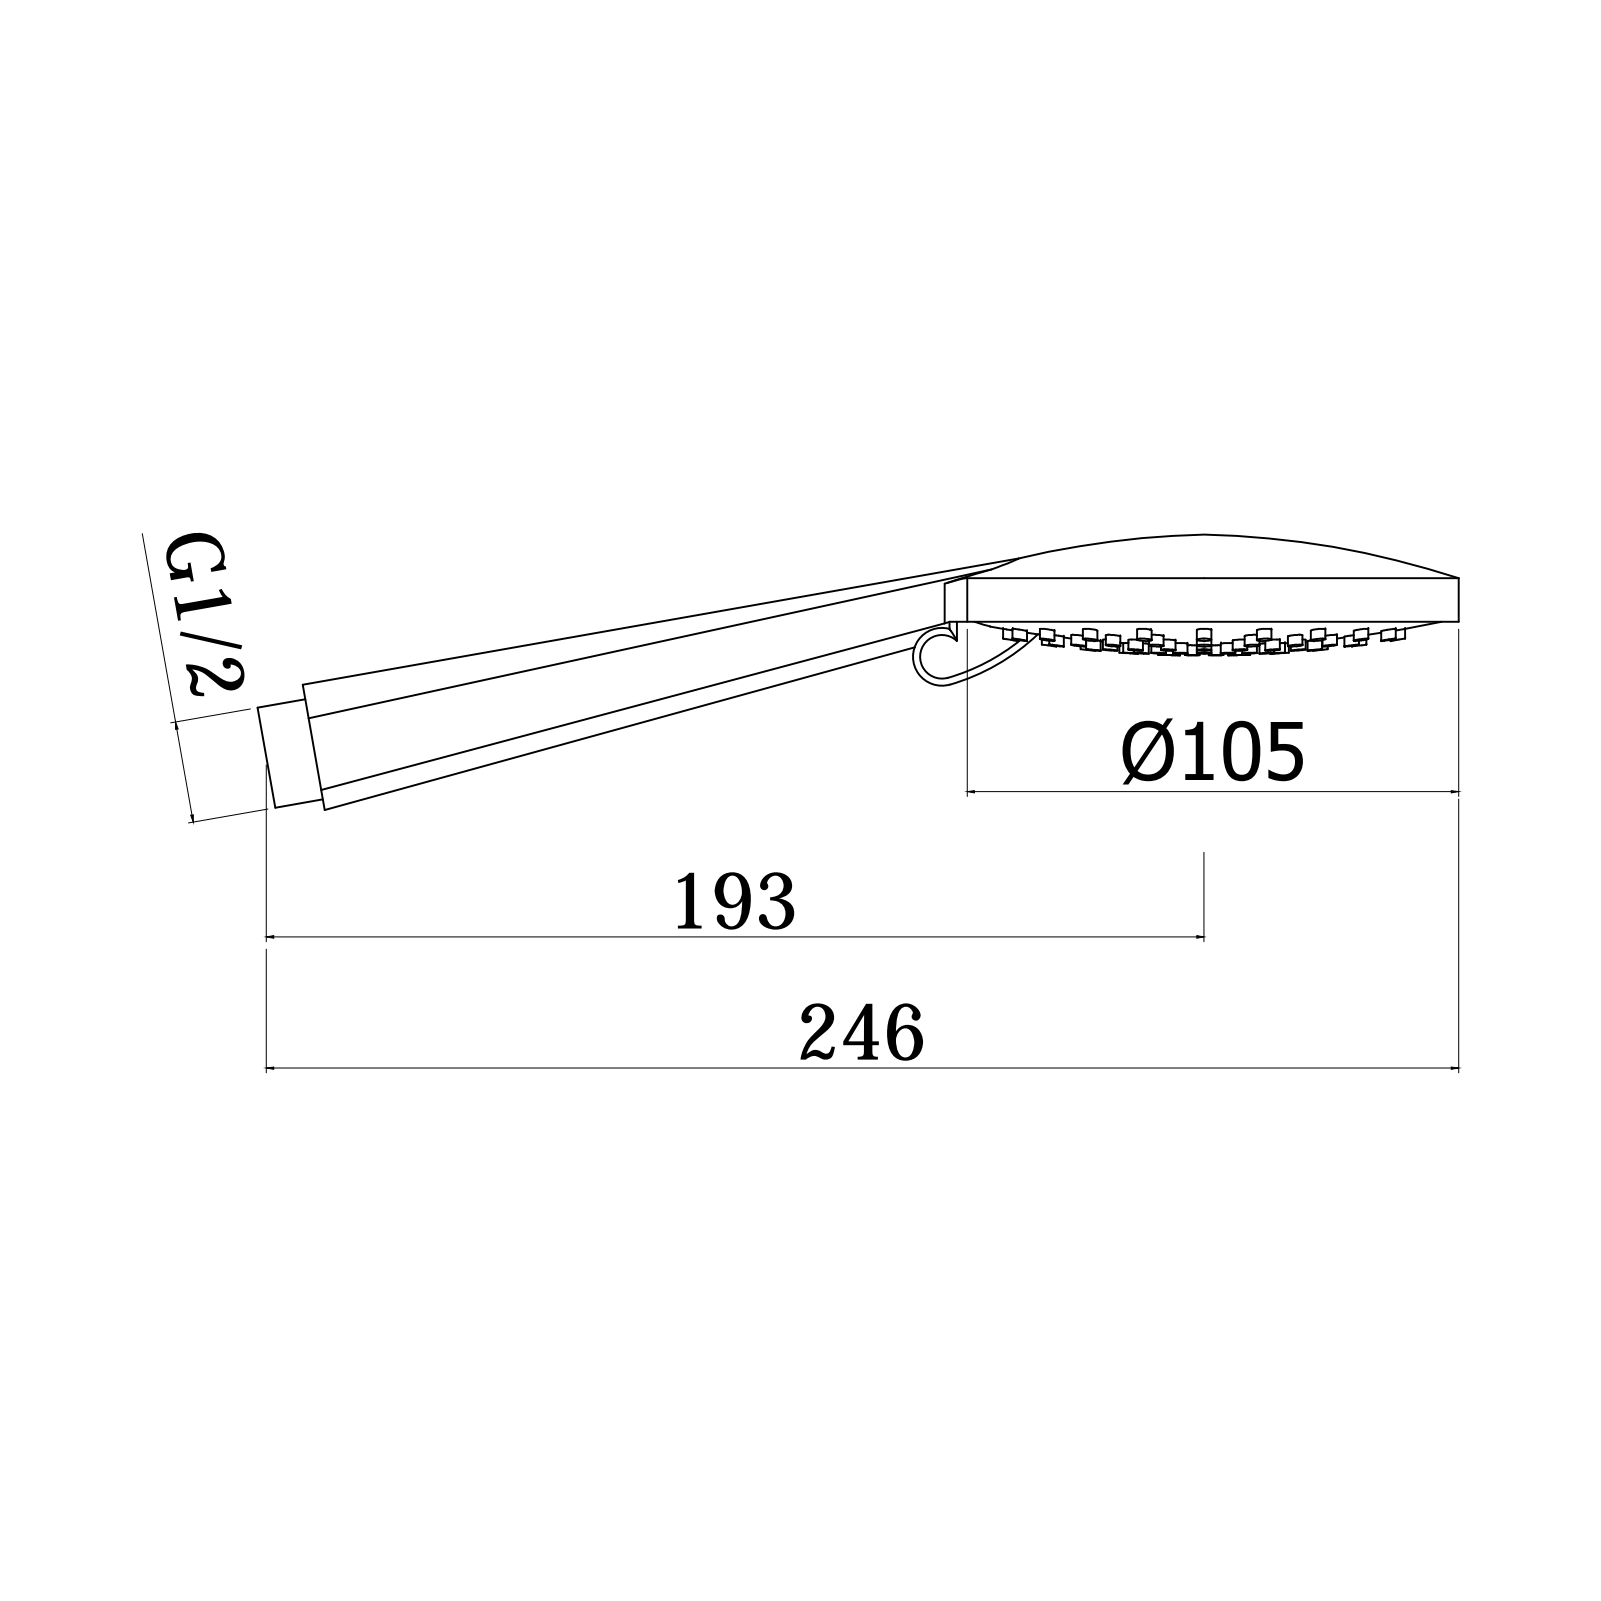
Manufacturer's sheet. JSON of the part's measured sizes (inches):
{"part_name": "ZDOC104CR", "step_written_by": "CREO PARAMETRIC BY PTC INC, 2020044 (CONFIG_CONTROL_DESIGN)", "units": "inches", "bodies": {"solids": 0, "faces": 299, "planar": 8, "cylindrical": 188, "other": 103}, "overall_size": [9.757, 4.134, 2.238], "round_bosses_or_shafts": [[0.118, 90], [4.134, 1], [0.827, 1]], "partial_cylinders_radius": [[0.024, 4], [0.236, 1]], "face_to_face_distances": [0.394, 0.138]}
